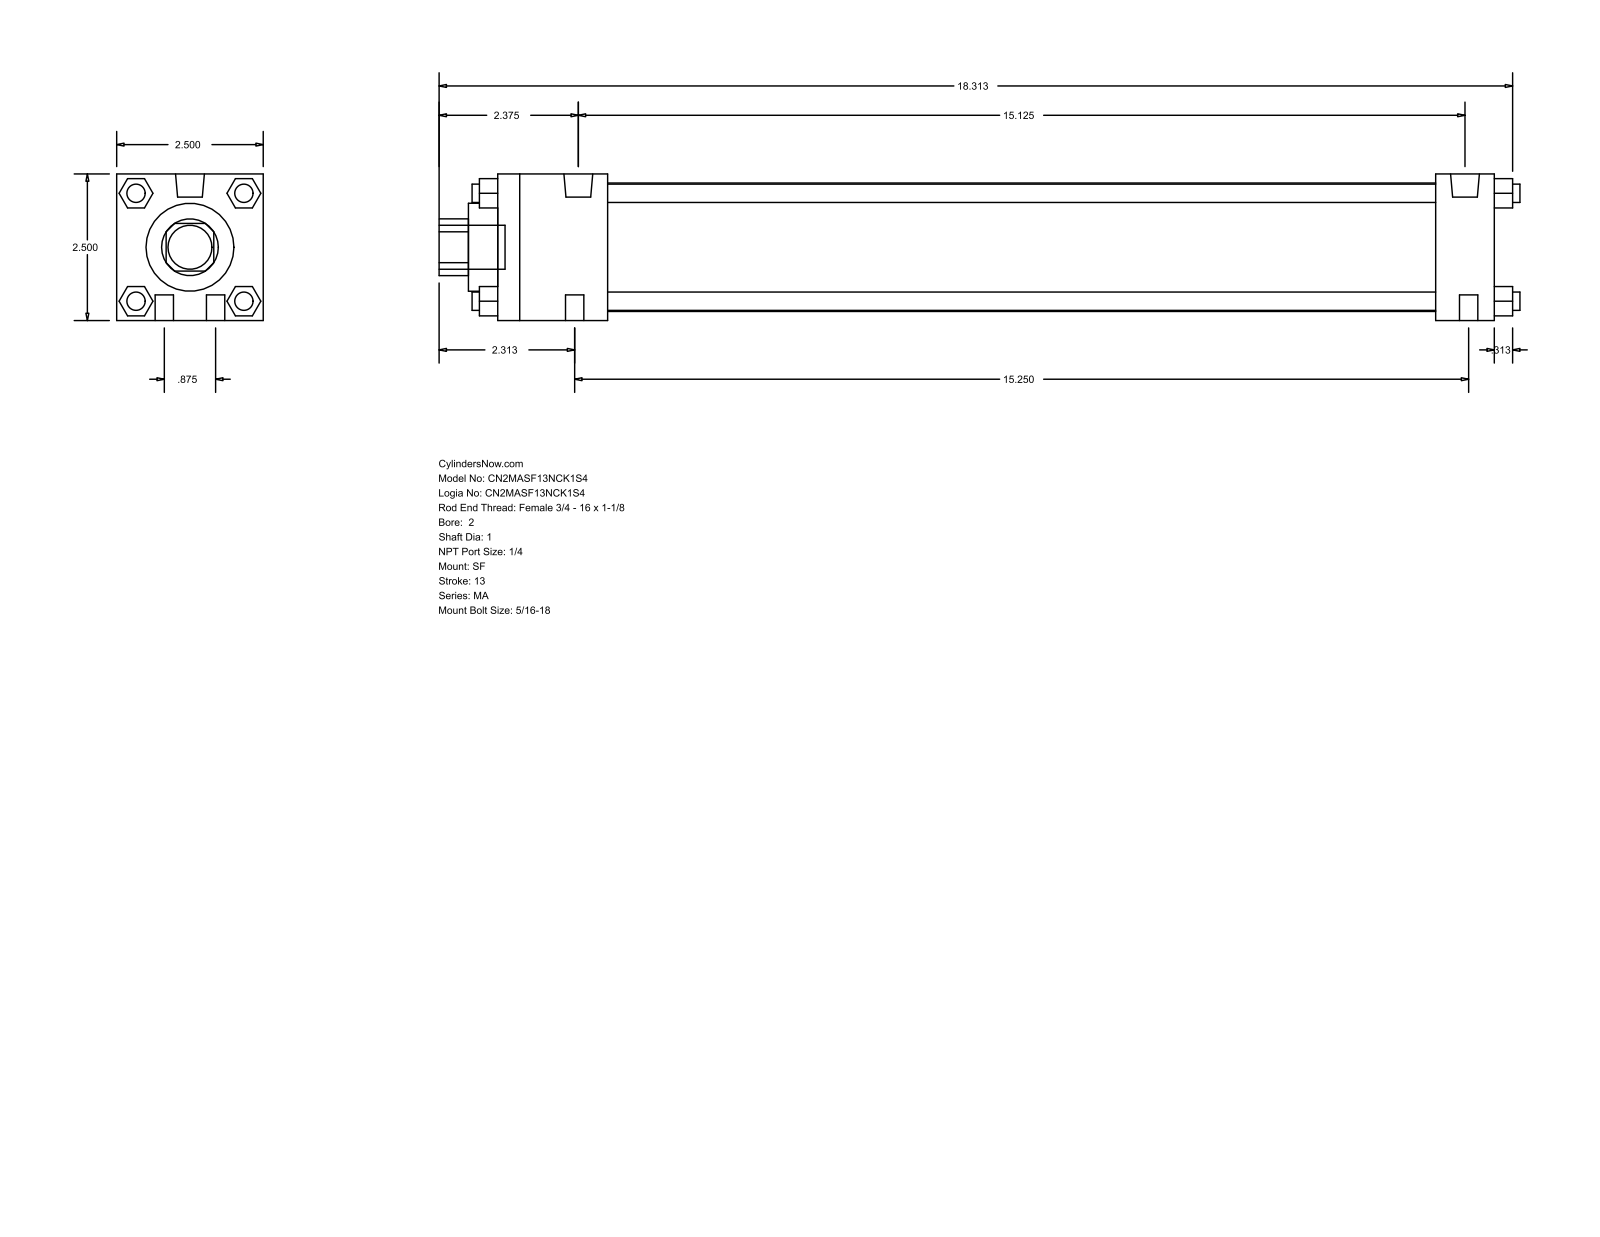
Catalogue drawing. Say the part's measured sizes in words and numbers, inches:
The part is named "MA_SF__0200_1". Its 3-D file was written by "GSSL Pune (CONFIG_CONTROL_DESIGN)". It is 0 solids with 124 faces: 94 planar, 30 cylindrical and 0 other. Overall it measures 18.437 by 2.5 by 2.5 inches. Round holes: 1 of diameter 1, 1 of diameter 1.5, 1 of diameter 2.19. Round bosses or shafts: 10 of diameter 0.313, 2 of diameter 0.492, 1 of diameter 0.75. Partial cylindrical surfaces (rounded edges, fillets, slot ends): 1 of radius 0.484. The main face-to-face distances are 2.5, 17, 0.5, 1, 16, 1.875, 14.125, 15.125, 0.92, 1.593.
